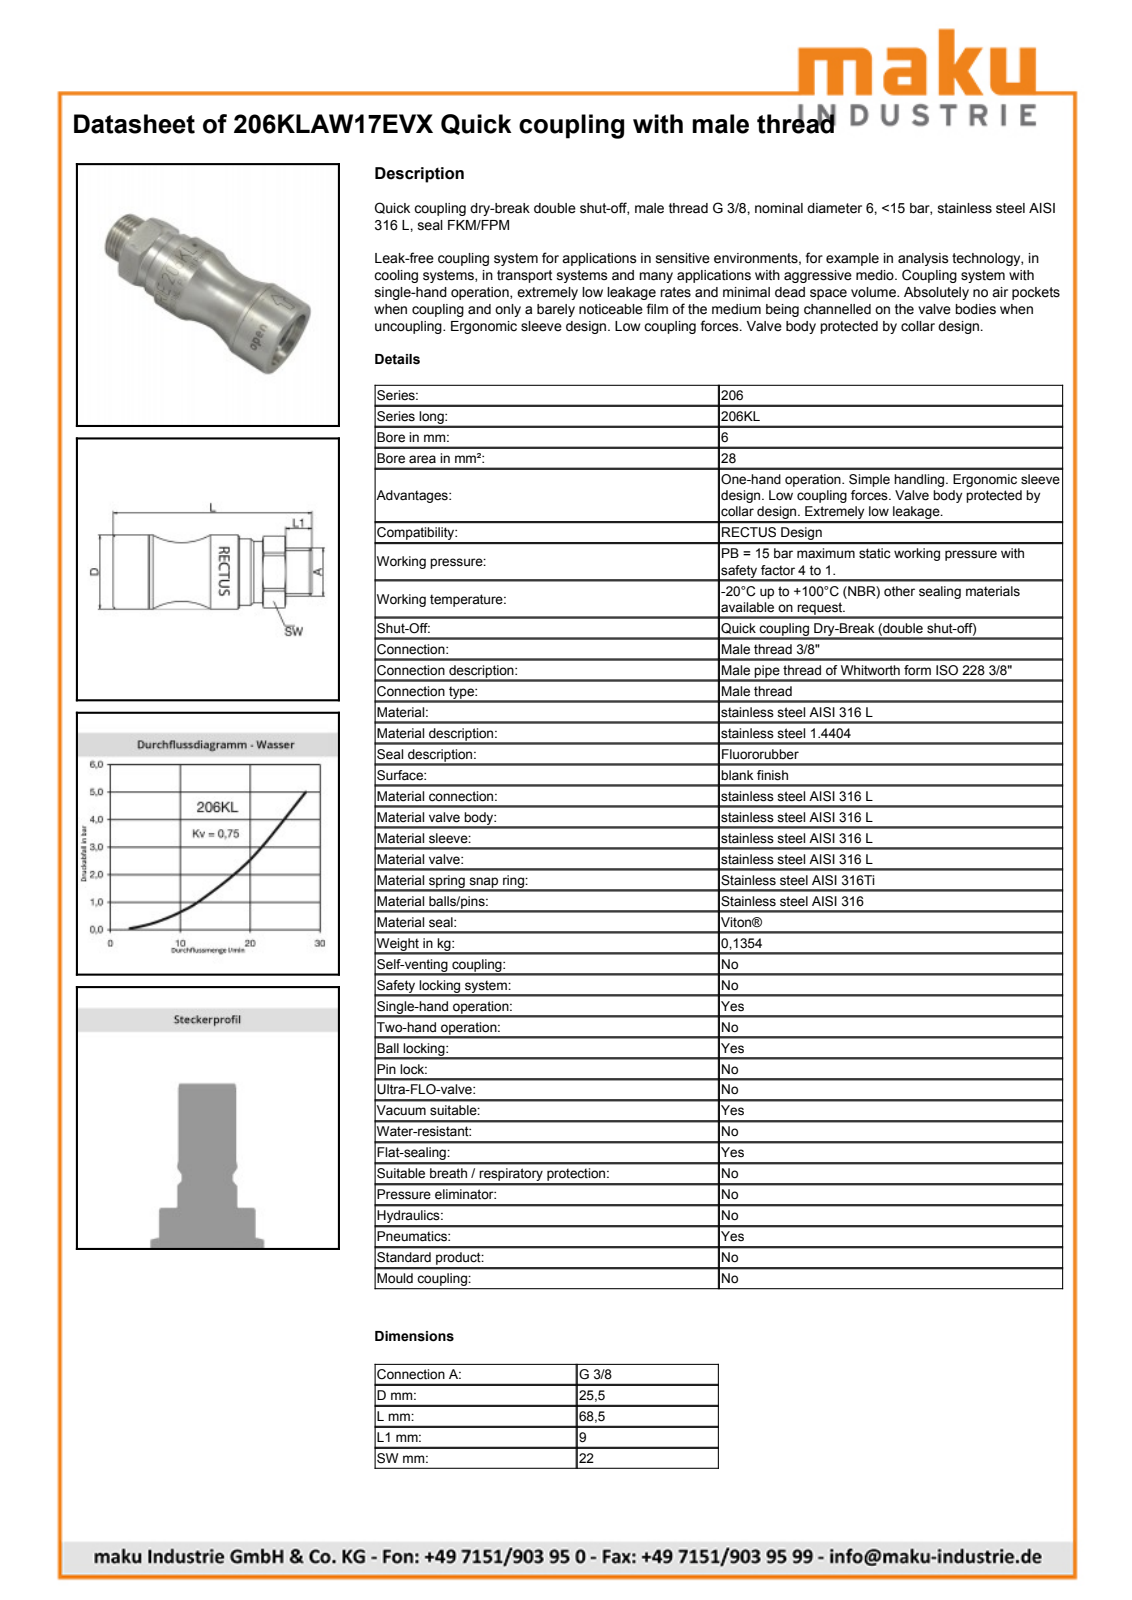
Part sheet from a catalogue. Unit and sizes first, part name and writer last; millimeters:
Units: millimetres
Overall size (bounding box): 68.5 × 25.5 × 25.5
Round holes (diameter × count): ⌀15.65 ×1, ⌀18.1 ×1, ⌀18.15 ×1, ⌀18.25 ×1, ⌀19.7 ×1, ⌀20.05 ×1, ⌀20.9 ×1, ⌀21.3 ×1, ⌀23.1 ×1, ⌀23.55 ×1, ⌀24.1 ×1
Round bosses / shafts (diameter × count): ⌀25.5 ×1, ⌀25.3 ×1, ⌀23.4 ×1, ⌀23 ×1, ⌀21 ×1, ⌀20 ×1, ⌀18 ×1, ⌀16.66 ×1
Partial cylindrical surfaces — rounded edges, fillets, slot ends (radius × count): R12.4 ×1
Main face-to-face distances: 68.5, 22, 59.5, 9, 4.1, 8, 4.65, 1.3, 58.2, 67.2
Volume: 23 569 mm³ · Surface area: 13 796 mm²
Bodies: 1 solid, 1177 faces (416 planar, 148 cylindrical, 613 other)
Part name (STEP PRODUCT): D107904
STEP written by: Autodesk Inventor 2013 (AUTOMOTIVE_DESIGN)
